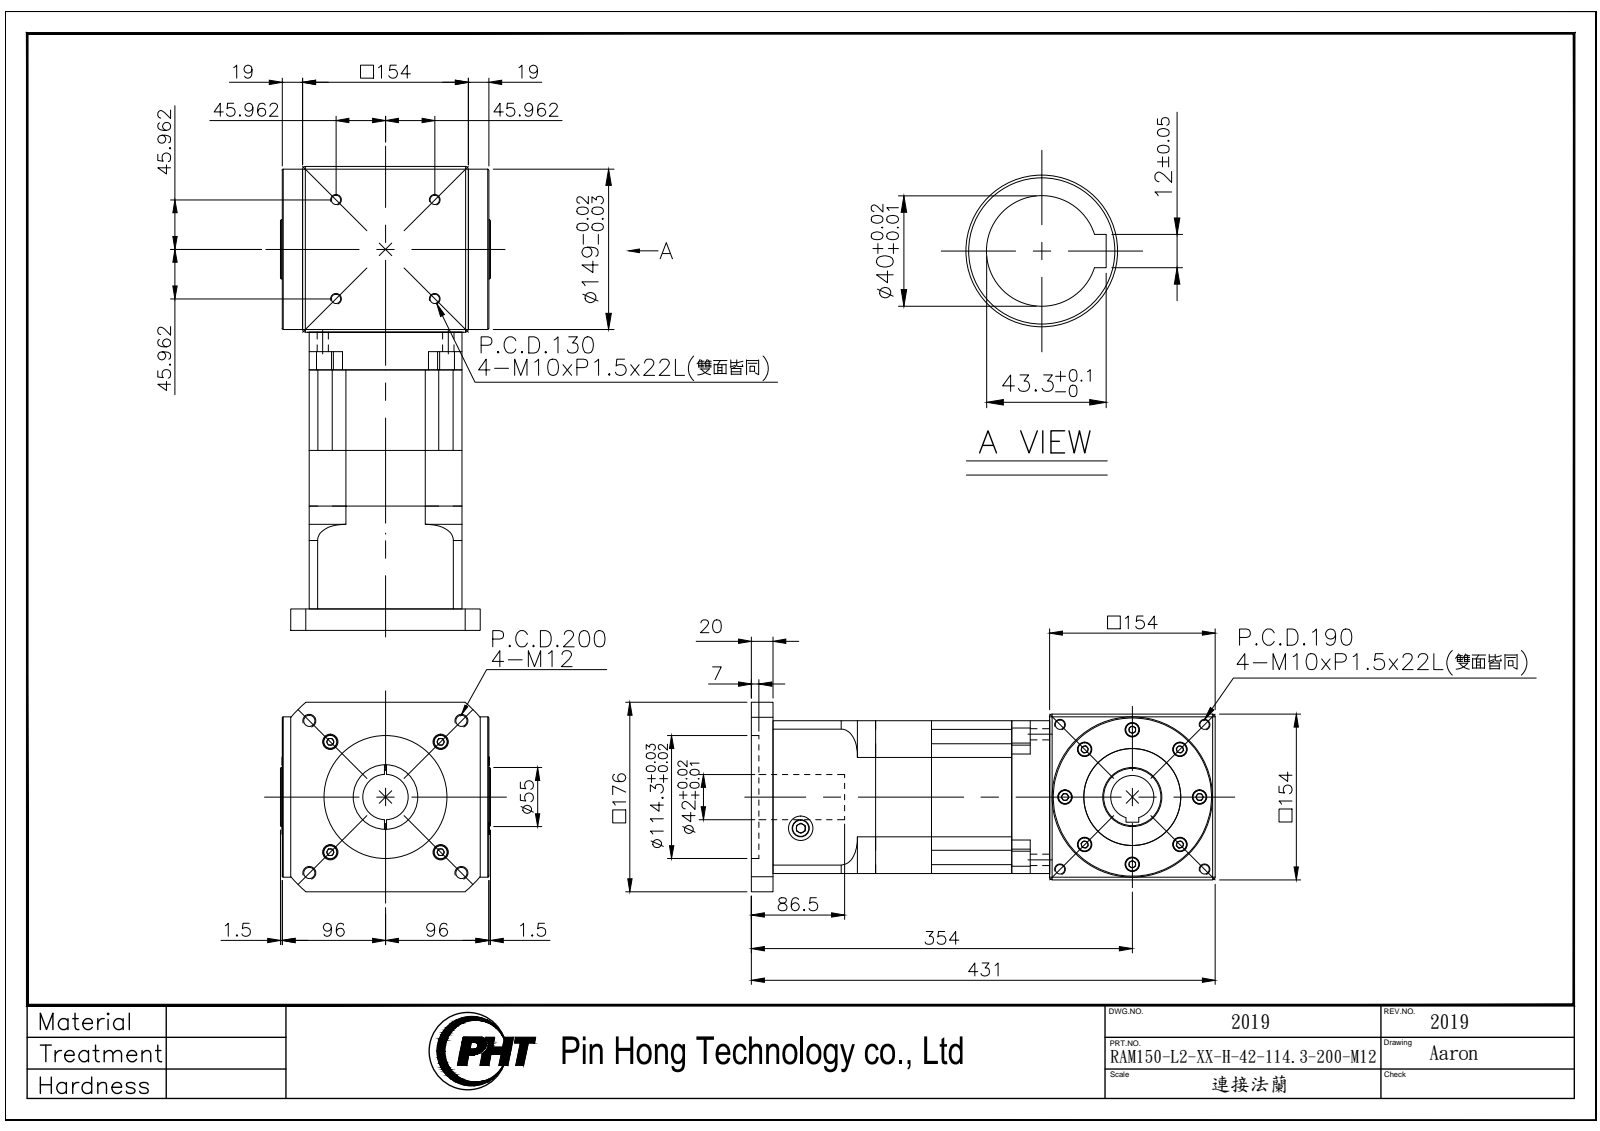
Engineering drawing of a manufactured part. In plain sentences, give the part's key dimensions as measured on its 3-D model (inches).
The part is named "RAM150-L2-XX-H-42-114.3-200-M12_2019". Its 3-D file was written by "SolidWorks 2016 (AUTOMOTIVE_DESIGN)". It is 5 solids with 885 faces: 421 planar, 316 cylindrical and 148 other. Overall it measures 16.969 by 7.677 by 6.929 inches. Its volume is 548.2 cubic inches and its surface area 1 009 square inches. Round holes: 12 of diameter 0.335, 12 of diameter 0.354, 12 of diameter 0.551, 8 of diameter 0.433, 8 of diameter 0.689, 4 of diameter 0.268, 4 of diameter 0.402, 4 of diameter 0.413, 2 of diameter 0.886, 1 of diameter 1.575, 1 of diameter 1.598, 1 of diameter 1.654. Round bosses or shafts: 12 of diameter 0.63, 4 of diameter 0.512, 1 of diameter 5.866, 1 of diameter 5.118, 1 of diameter 3.543, 1 of diameter 2.913, 1 of diameter 2.165. Partial cylindrical surfaces (rounded edges, fillets, slot ends): 4 of radius 0.394, 1 of radius 3.15, 1 of radius 3.74, 1 of radius 4.228, 1 of radius 4.528. The main face-to-face distances are 0.236, 5.827, 6.063, 5.591, 2.039, 4.98, 2.941, 6.358, 4.319, 1.378. The hole center spacings are 2.795, 0.737, 0.74, 0.908, 1.433, 1.883, 2.651, 3.265.
